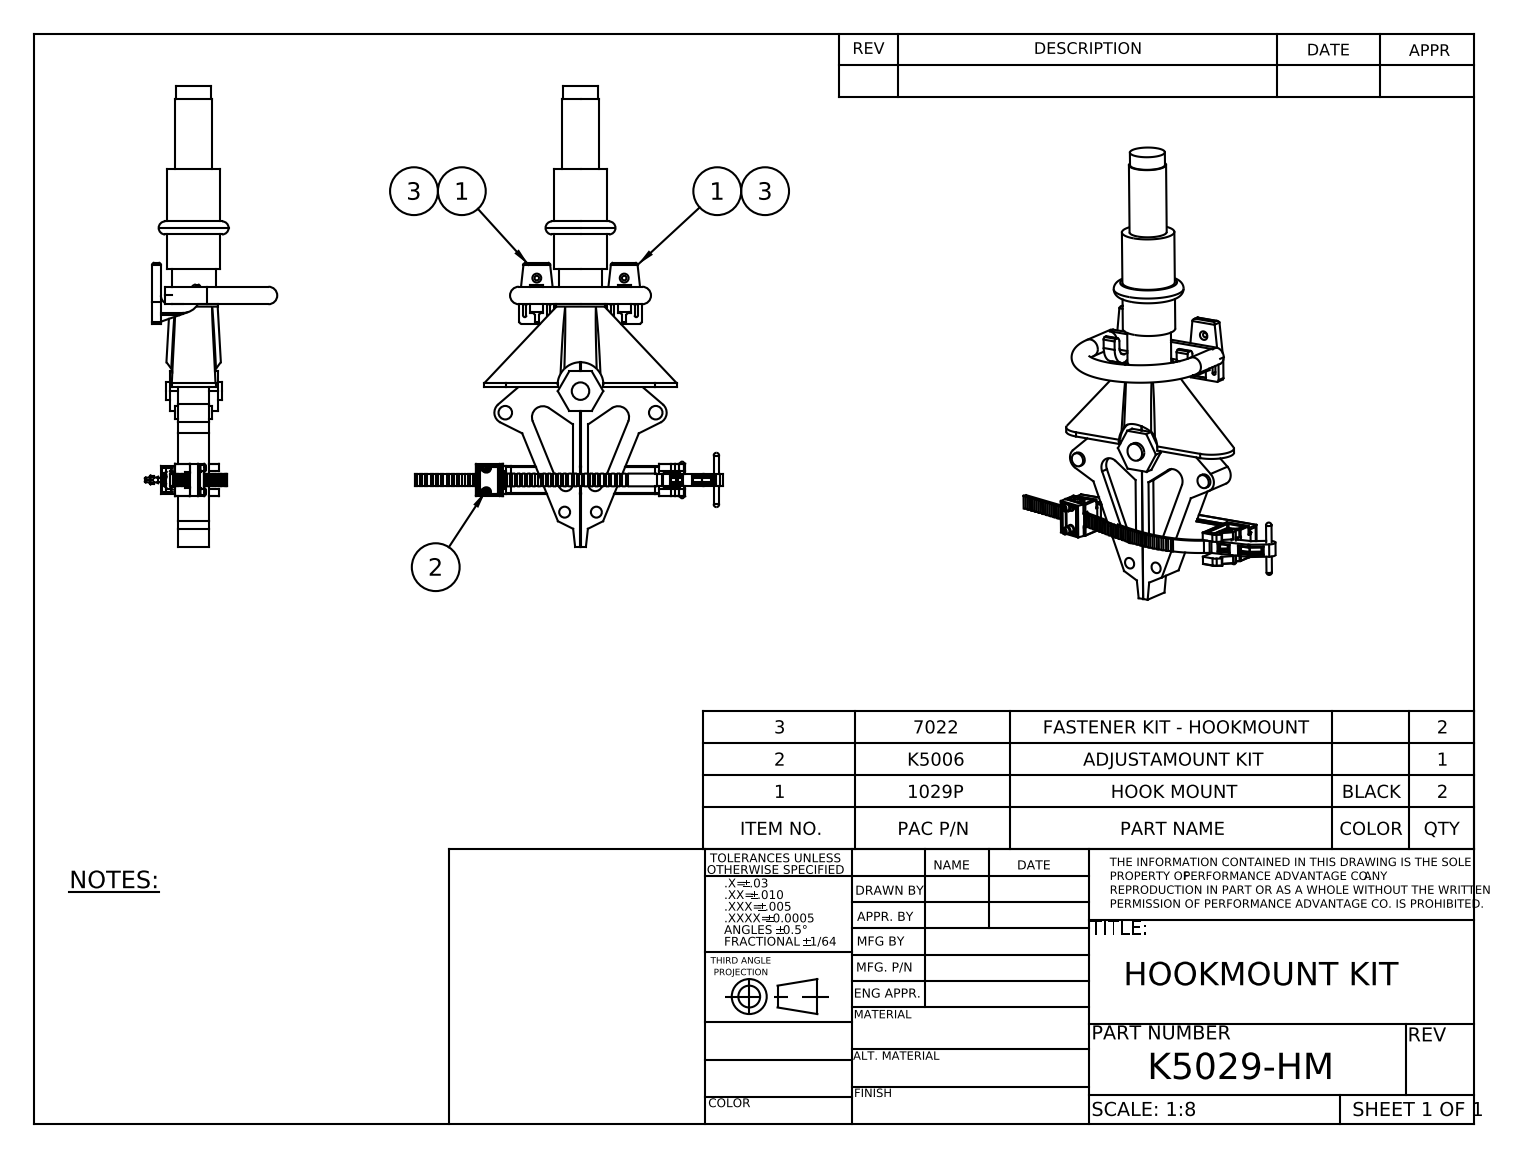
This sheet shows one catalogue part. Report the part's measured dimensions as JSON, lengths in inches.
{"part_name": "1006-3; .25-20 Nylok Nut_MSHXNUT 0.250-20-S-N; .25-20 x 1.0 lg Hex Bolt_HBOLT 0.2500-20x1x1-N; 2035 Pack_10\" apart (+8 more)", "step_written_by": "SolidWorks 2010 (CONFIG_CONTROL_DESIGN)", "units": "inches", "bodies": {"solids": 27, "faces": 1433, "planar": 619, "cylindrical": 472, "other": 342}, "overall_size": [26.375, 17.642, 7.578], "volume_in3": 155.3, "surface_area_in2": 1113, "round_holes": [[0.201, 6], [0.25, 4], [0.266, 2], [0.269, 2], [0.288, 2], [0.313, 2], [0.625, 2], [0.75, 2], [0.26, 1], [0.291, 1], [0.625, 1], [0.64, 1]], "round_bosses_or_shafts": [[0.25, 5], [0.375, 4], [1, 3], [0.774, 2], [0.625, 2], [0.404, 2], [3, 1], [2.125, 1]], "partial_cylinders_radius": [[0.062, 66], [0.063, 51], [0.031, 36], [0.02, 30], [0.125, 16], [0.06, 8], [0.095, 8], [0.25, 5]], "face_to_face_distances": [0.5, 2.75, 1, 1.75, 1.25, 0.187, 0.75, 1.5, 0.188, 0.813], "hole_center_spacings": [1.433, 4.488, 6.113, 6.187, 10.654, 11.815, 12.669, 13.165]}
